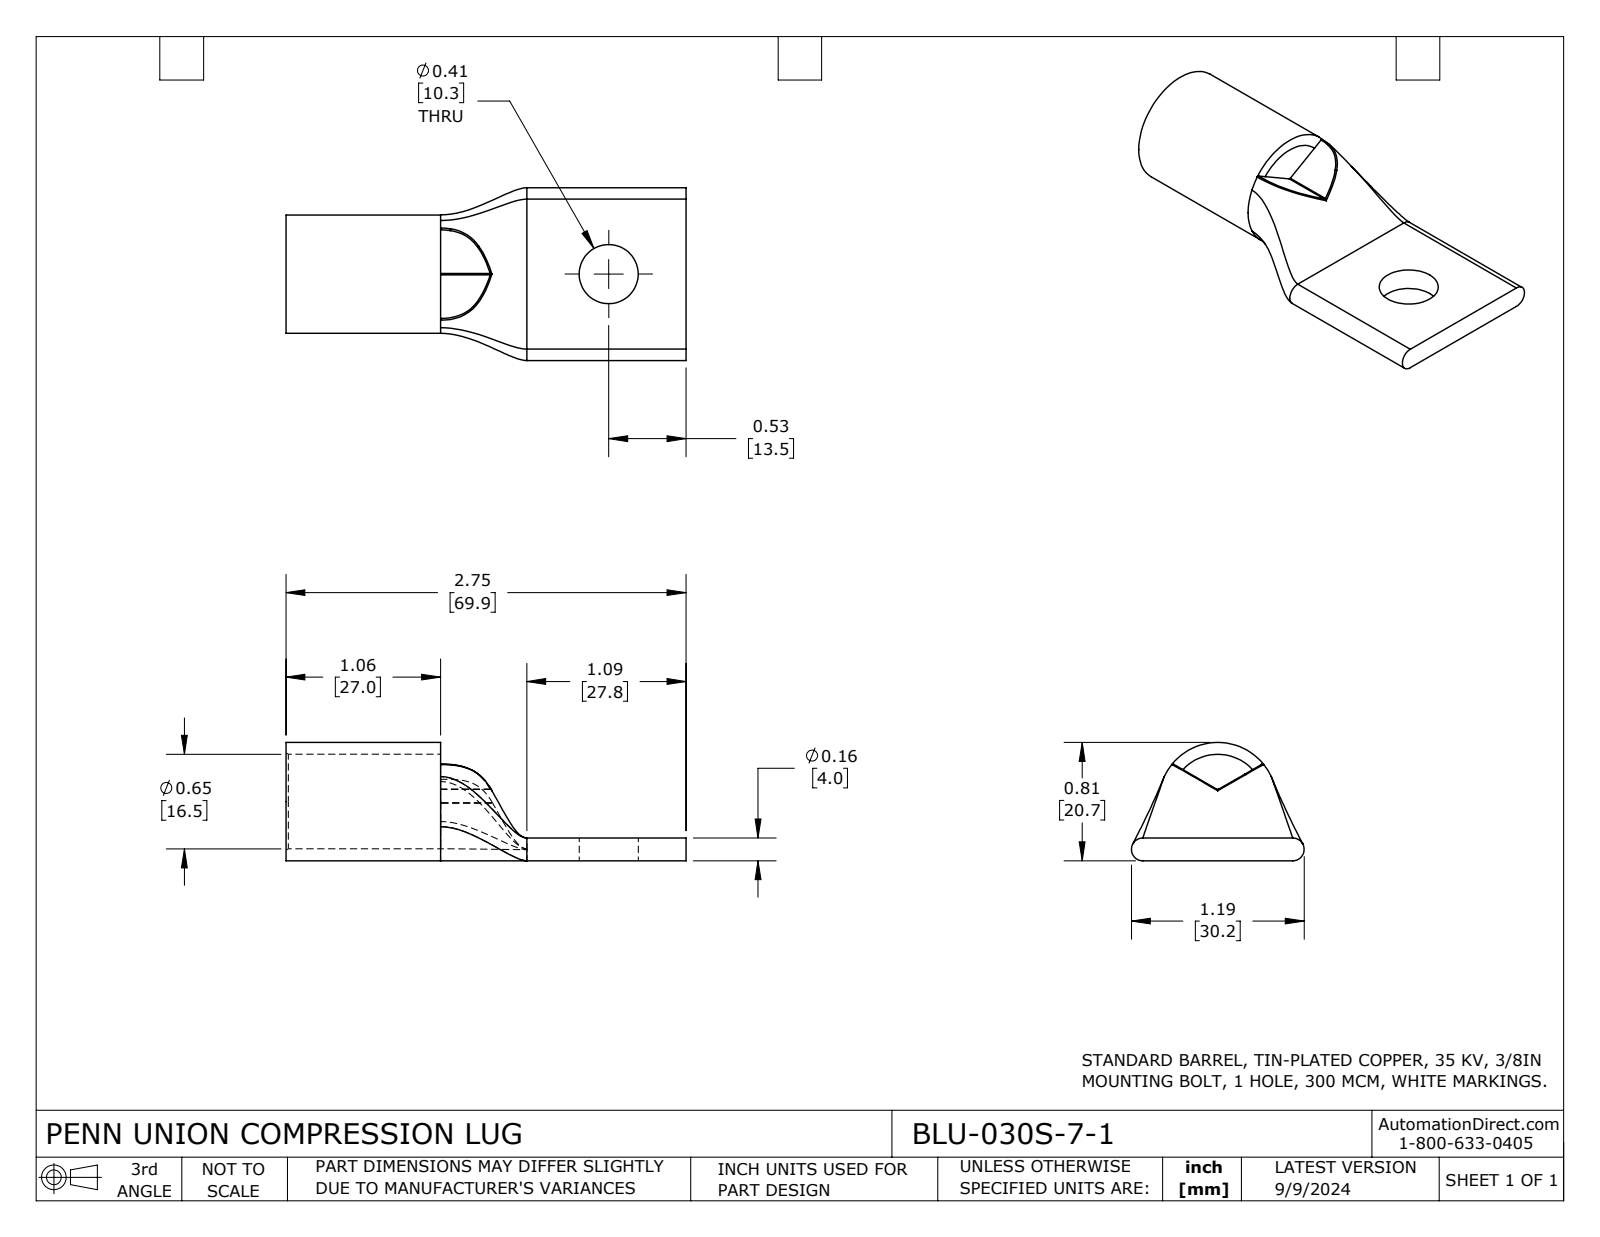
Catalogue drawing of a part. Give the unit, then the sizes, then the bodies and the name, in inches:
Units: inches
Overall size (bounding box): 2.75 × 1.188 × 0.813
Round holes (diameter × count): ⌀0.406 ×1, ⌀0.65 ×1
Round bosses / shafts (diameter × count): ⌀0.813 ×1
Partial cylindrical surfaces — rounded edges, fillets, slot ends (radius × count): R0.01 ×2, R0.078 ×2
Main face-to-face distances: 0.156, 0.081, 2.75, 1.063, 1.687, 1.656, 0.593, 1.094
Volume: 0.48 in³ · Surface area: 11.16 in²
Bodies: 1 solid, 37 faces (11 planar, 11 cylindrical, 15 other)
Part name (STEP PRODUCT): BLU-030S-7-1
STEP written by: SolidWorks 2023 (CONFIG_CONTROL_DESIGN)
